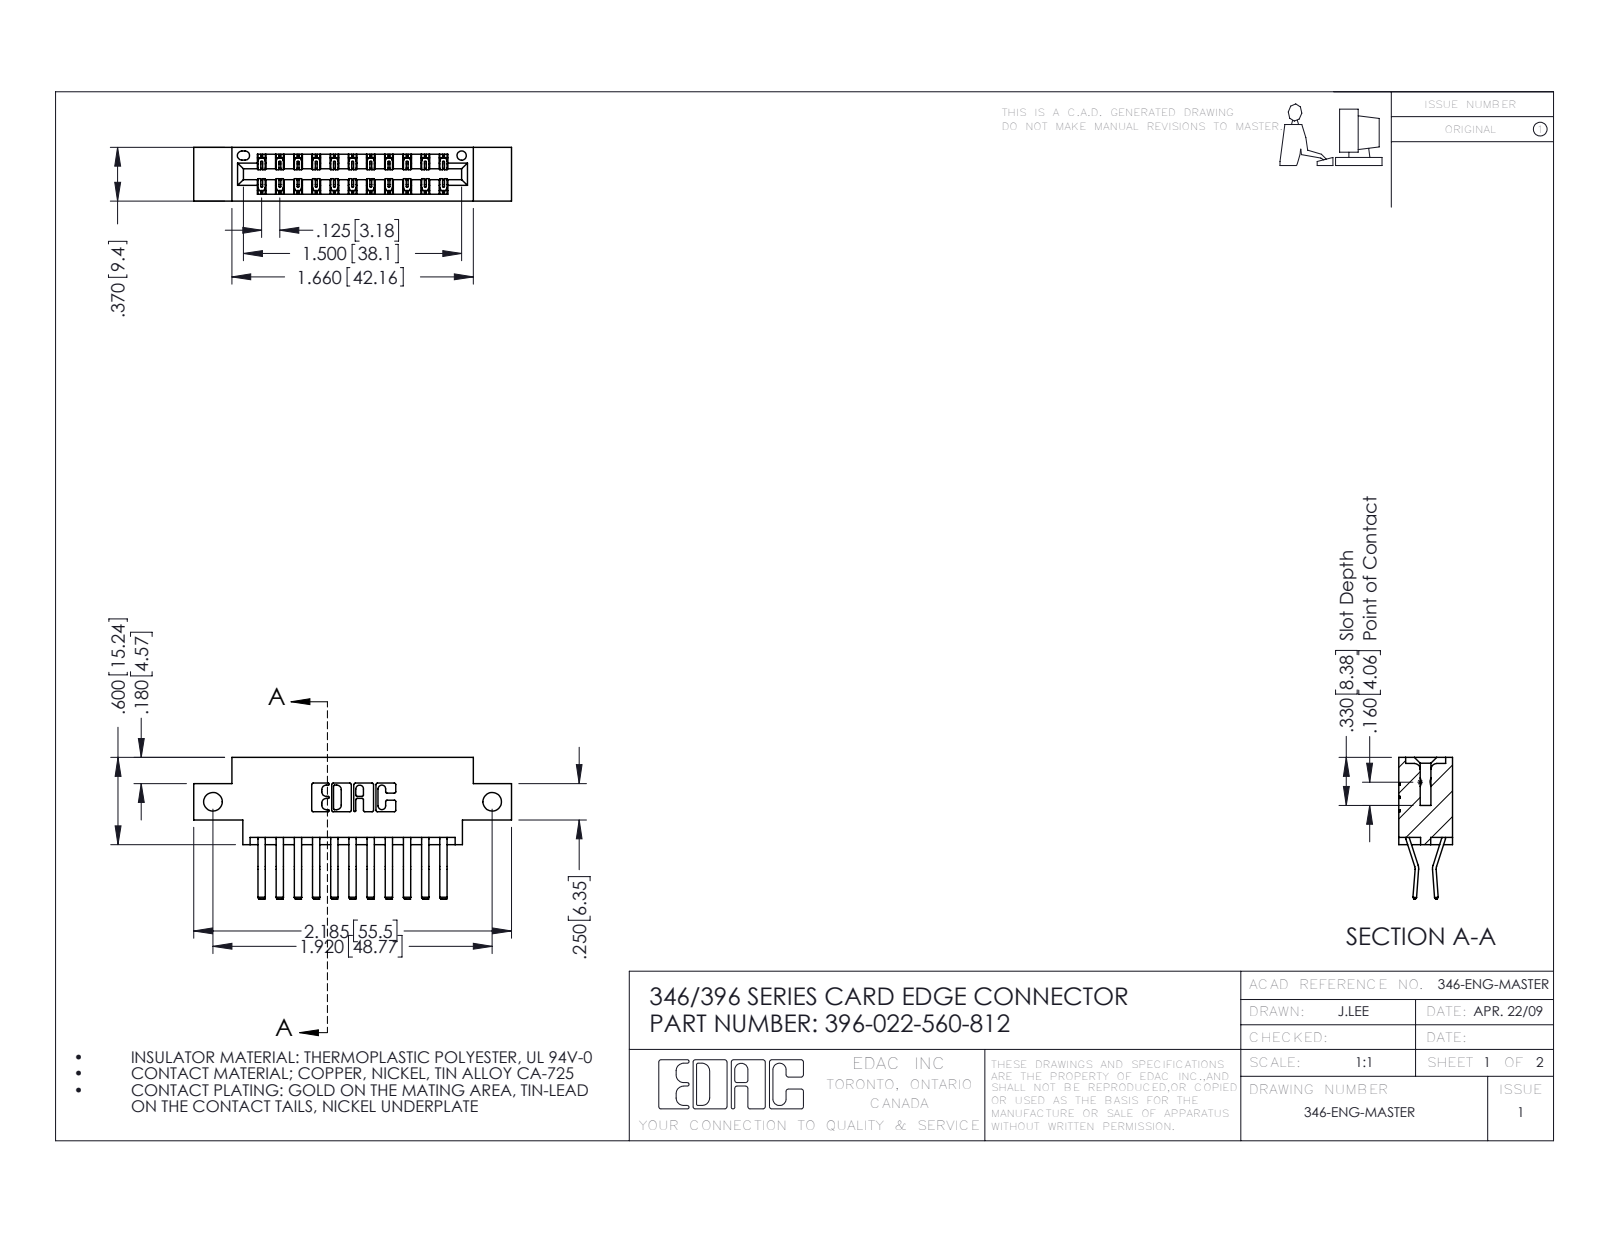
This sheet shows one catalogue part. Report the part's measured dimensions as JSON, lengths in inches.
{"part_name": "346 Part_0.170 Offset - Side Mount; 345-292-001_560 Tail; 396-022-560-812", "step_written_by": "SolidWorks 2016 (CONFIG_CONTROL_DESIGN)", "units": "inches", "bodies": {"solids": 23, "faces": 1314, "planar": 850, "cylindrical": 464, "other": 0}, "overall_size": [2.185, 0.975, 0.37], "volume_in3": 0.31, "surface_area_in2": 10.72, "round_holes": [[0.128, 2], [0.064, 1]], "partial_cylinders_radius": [[0.006, 33], [0.01, 22], [0.007, 6], [0.031, 6], [0.026, 3], [0.01, 2], [0.014, 2], [0.022, 2]], "face_to_face_distances": [0.25, 0.37, 0.048, 0.322, 0.025, 0.072, 0.298, 0.275, 0.148, 0.222], "hole_center_spacings": [1.92]}
